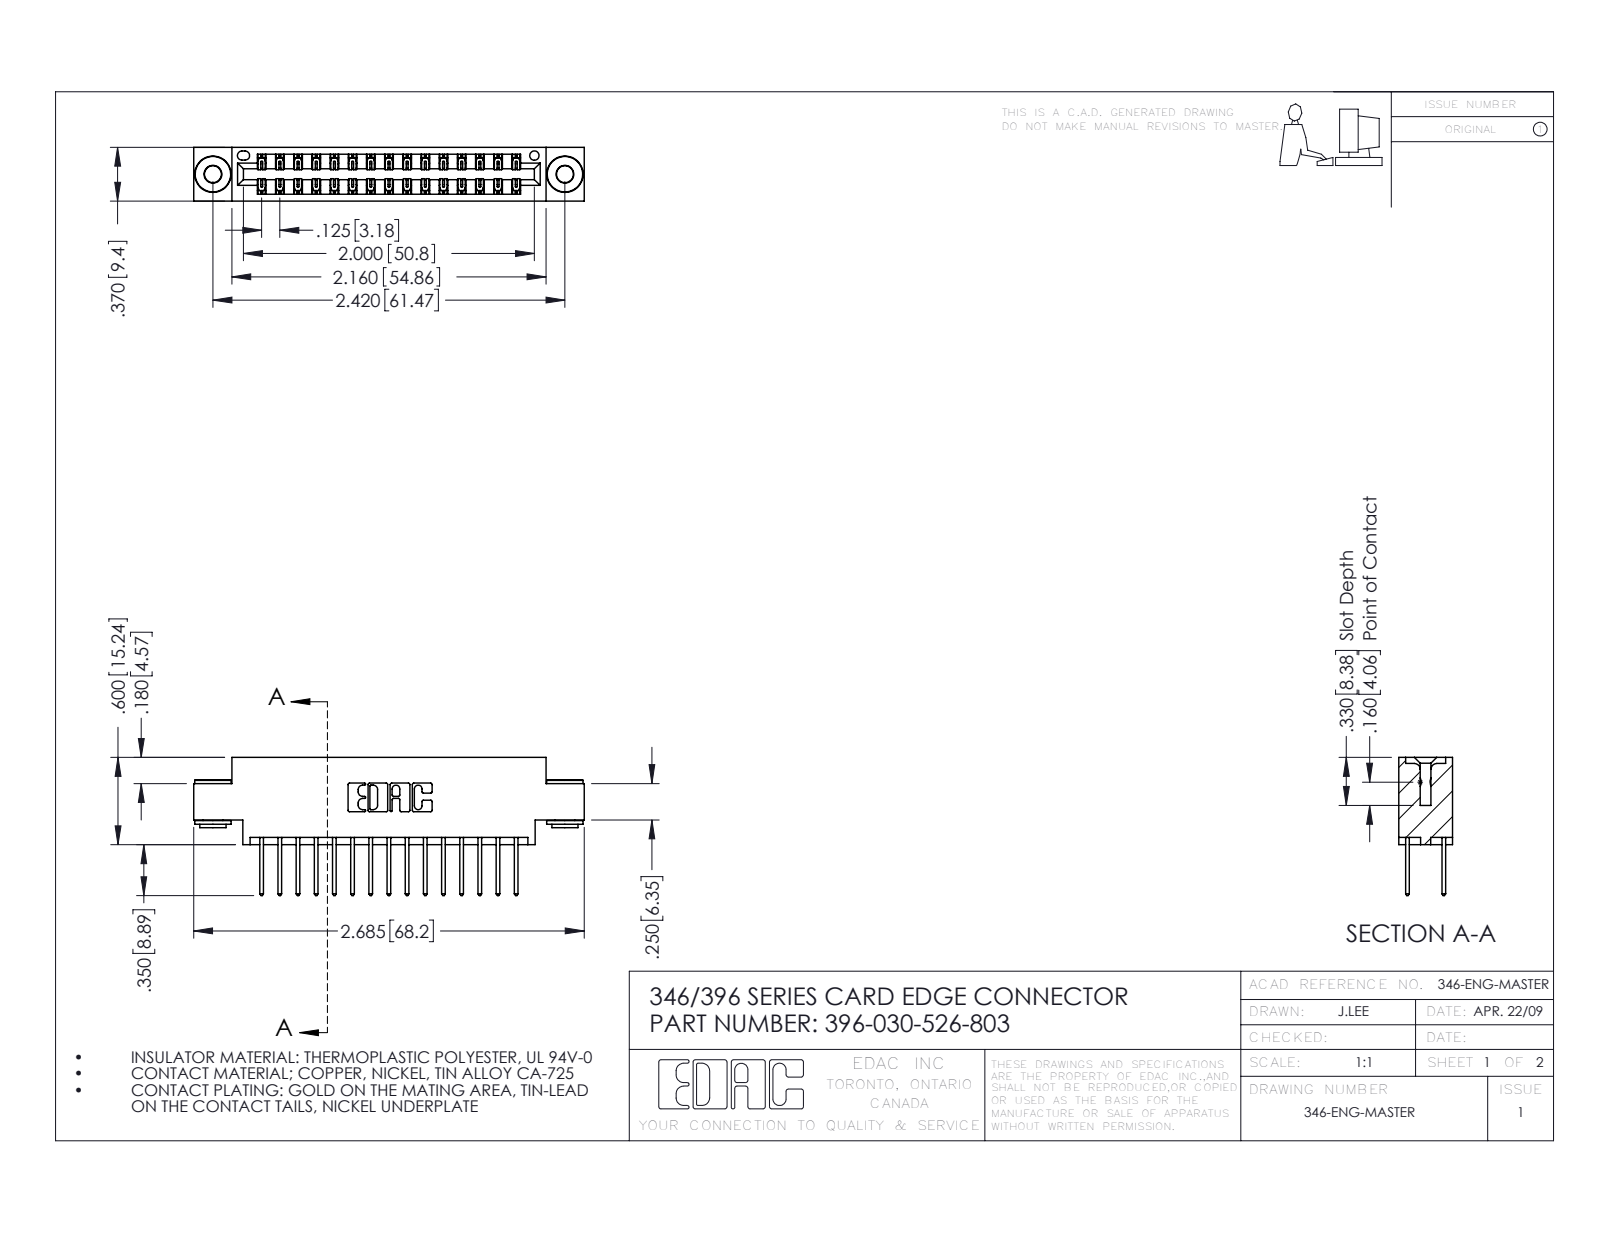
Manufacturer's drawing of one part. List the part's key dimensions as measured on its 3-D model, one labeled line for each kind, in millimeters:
Part name (STEP PRODUCT): 345-250-002_345-250-002-102; 396-030-526-803; 345-292-001_345-293-126; 346 Part_0.170 Offset - 0.156 Dia-TH
STEP written by: SolidWorks 2016 (CONFIG_CONTROL_DESIGN)
Units: millimetres
Bodies: 33 solids, 1724 faces (1140 planar, 576 cylindrical, 8 other)
Overall size (bounding box): 68.2 × 24.1 × 9.4
Volume: 6 360 mm³ · Surface area: 8 923 mm²
Round holes (diameter × count): ⌀2.9 ×2, ⌀4 ×2, ⌀1.6 ×1
Round bosses / shafts (diameter × count): ⌀6.4 ×2, ⌀4.6 ×2, ⌀3.5 ×2
Partial cylindrical surfaces — rounded edges, fillets, slot ends (radius × count): R0.2 ×45, R0.3 ×30, R0.3 ×22, R0.2 ×6, R0.8 ×6, R0.7 ×3, R0.4 ×2, R0.6 ×2
Main face-to-face distances: 1.2, 8.2, 6.4, 9.4, 0.6, 1.8, 7.6, 7, 3.8, 5.6
Hole centre spacings: 6.2, 56.2, 61.5
